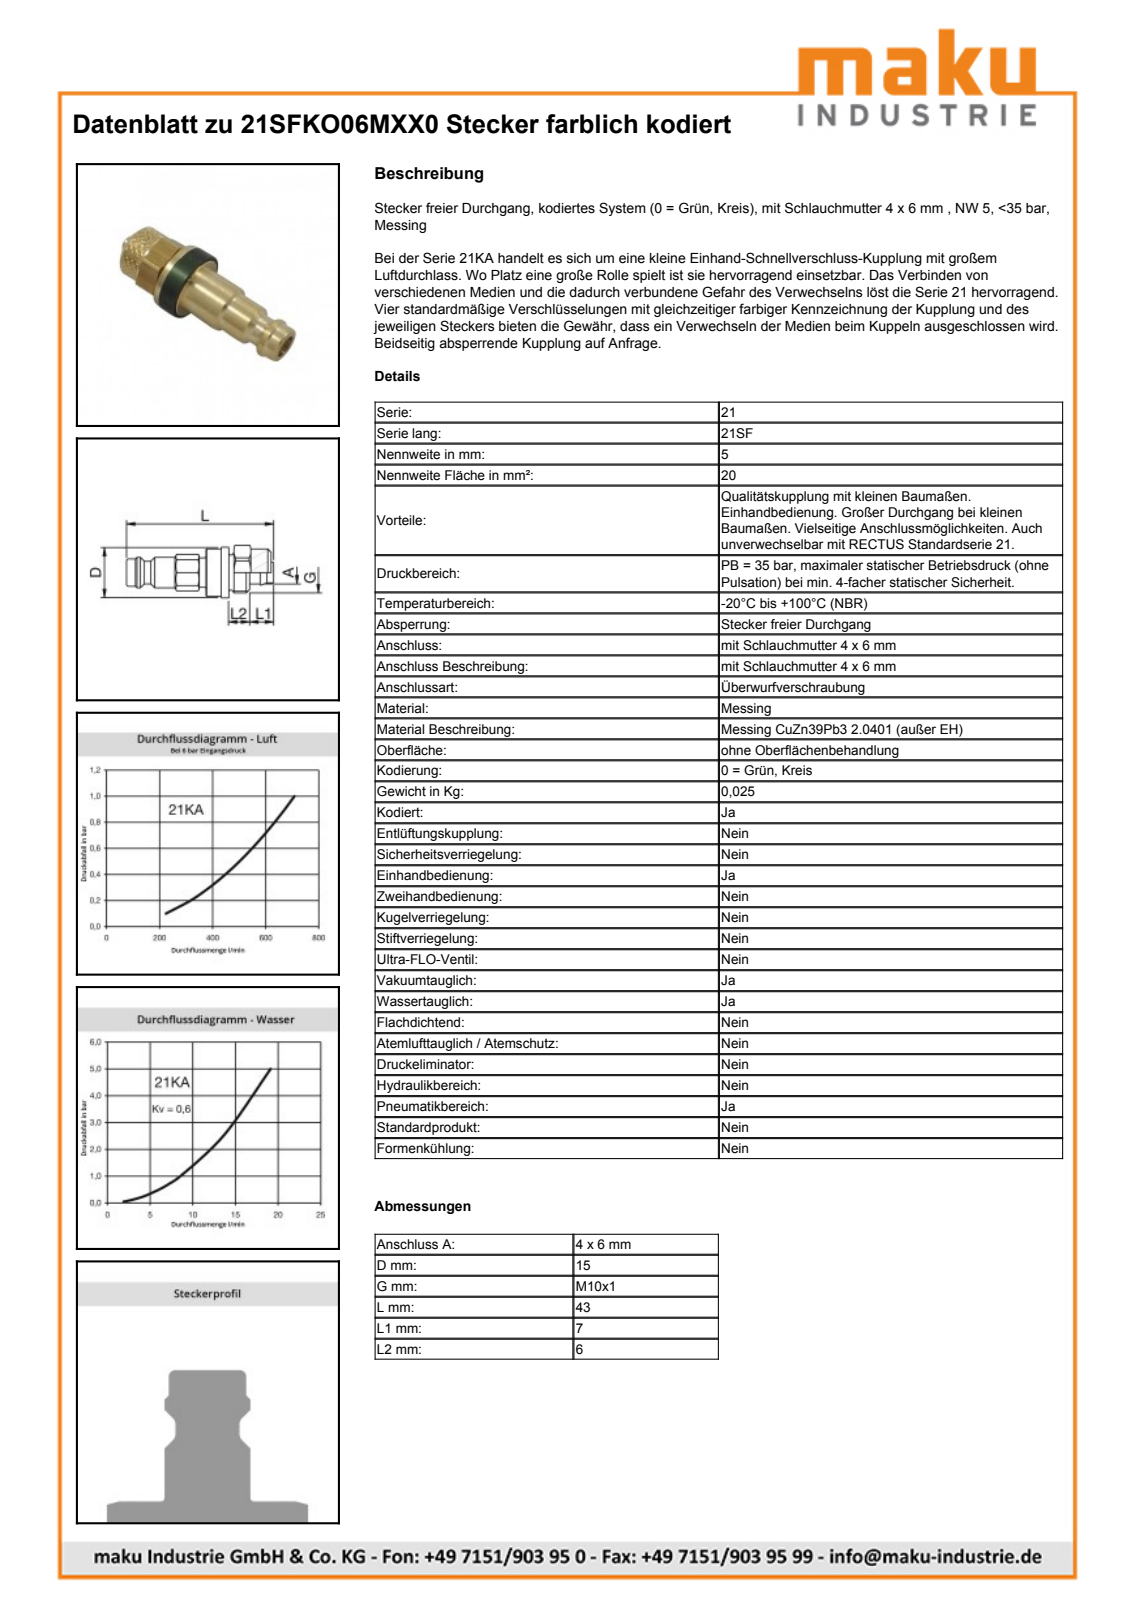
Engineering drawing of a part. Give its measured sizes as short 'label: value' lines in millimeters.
name: D107378; D107286; D102148; D103012
written by: Autodesk Inventor 2013 (AUTOMOTIVE_DESIGN)
unit: mm
bodies: 3 solids, 73 faces (17 planar, 26 cylindrical, 30 other)
size: 43.58 × 15.5 × 15.5
volume: 3 146 mm³; area: 3 499 mm²
holes: 1× ⌀2.95, 1× ⌀4.95, 1× ⌀6.2, 1× ⌀9.45, 1× ⌀13.85, 1× ⌀14.05
bosses: 1× ⌀15.5, 1× ⌀15, 1× ⌀14, 1× ⌀12, 1× ⌀10.4, 1× ⌀10, 1× ⌀9, 1× ⌀8.6
rounds: 1× R6.75
face distances: 12, 6.25, 1.75, 4.5, 13.83, 15.58, 20.08, 7.68, 6.15, 7.9
